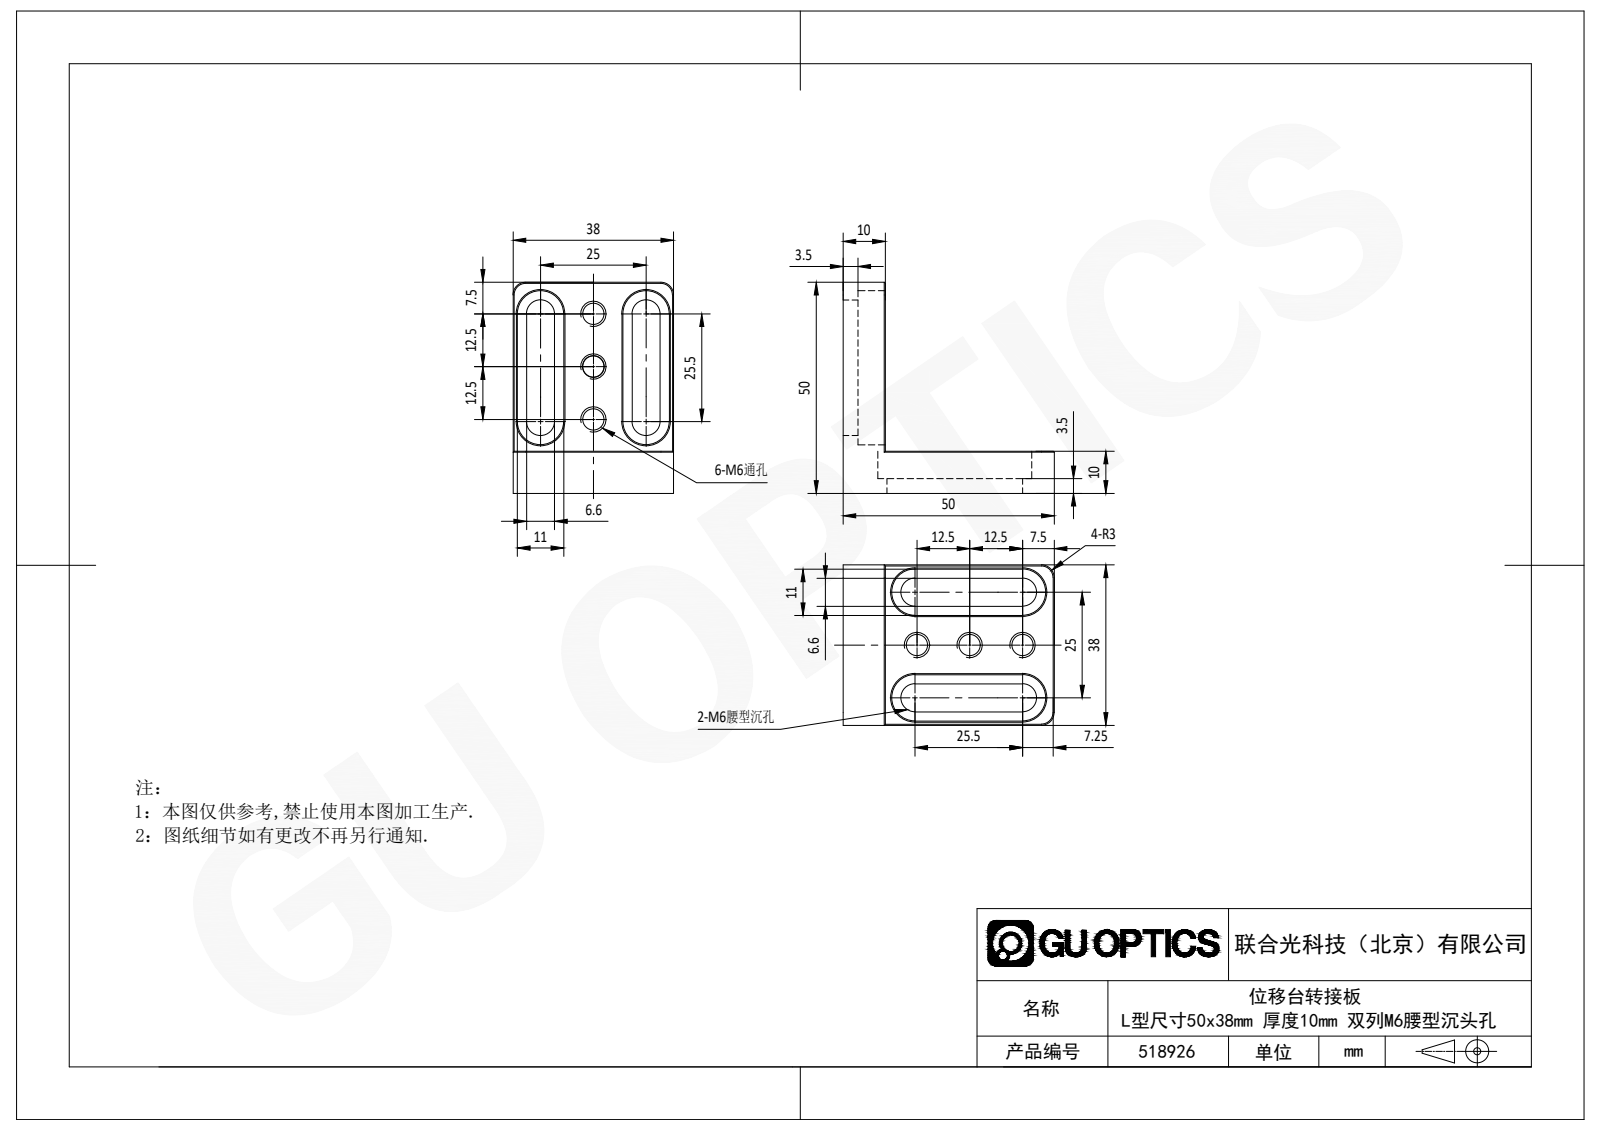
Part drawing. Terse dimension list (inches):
written by: SolidWorks 2020 (CONFIG_CONTROL_DESIGN)
unit: in
bodies: 1 solid, 90 faces (44 planar, 28 cylindrical, 18 other)
size: 1.969 × 1.969 × 1.496
volume: 1.236 in³; area: 17.92 in²
holes: 6× ⌀0.197, 1× ⌀0.201, 1× ⌀0.234
rounds: 8× R0.13, 8× R0.217, 4× R0.118
face distances: 0.394, 0.984, 1.496, 0.087, 0.346, 0.138, 0.256, 0.039, 0.472, 1.024
hole spacings: 0.492, 0.984
